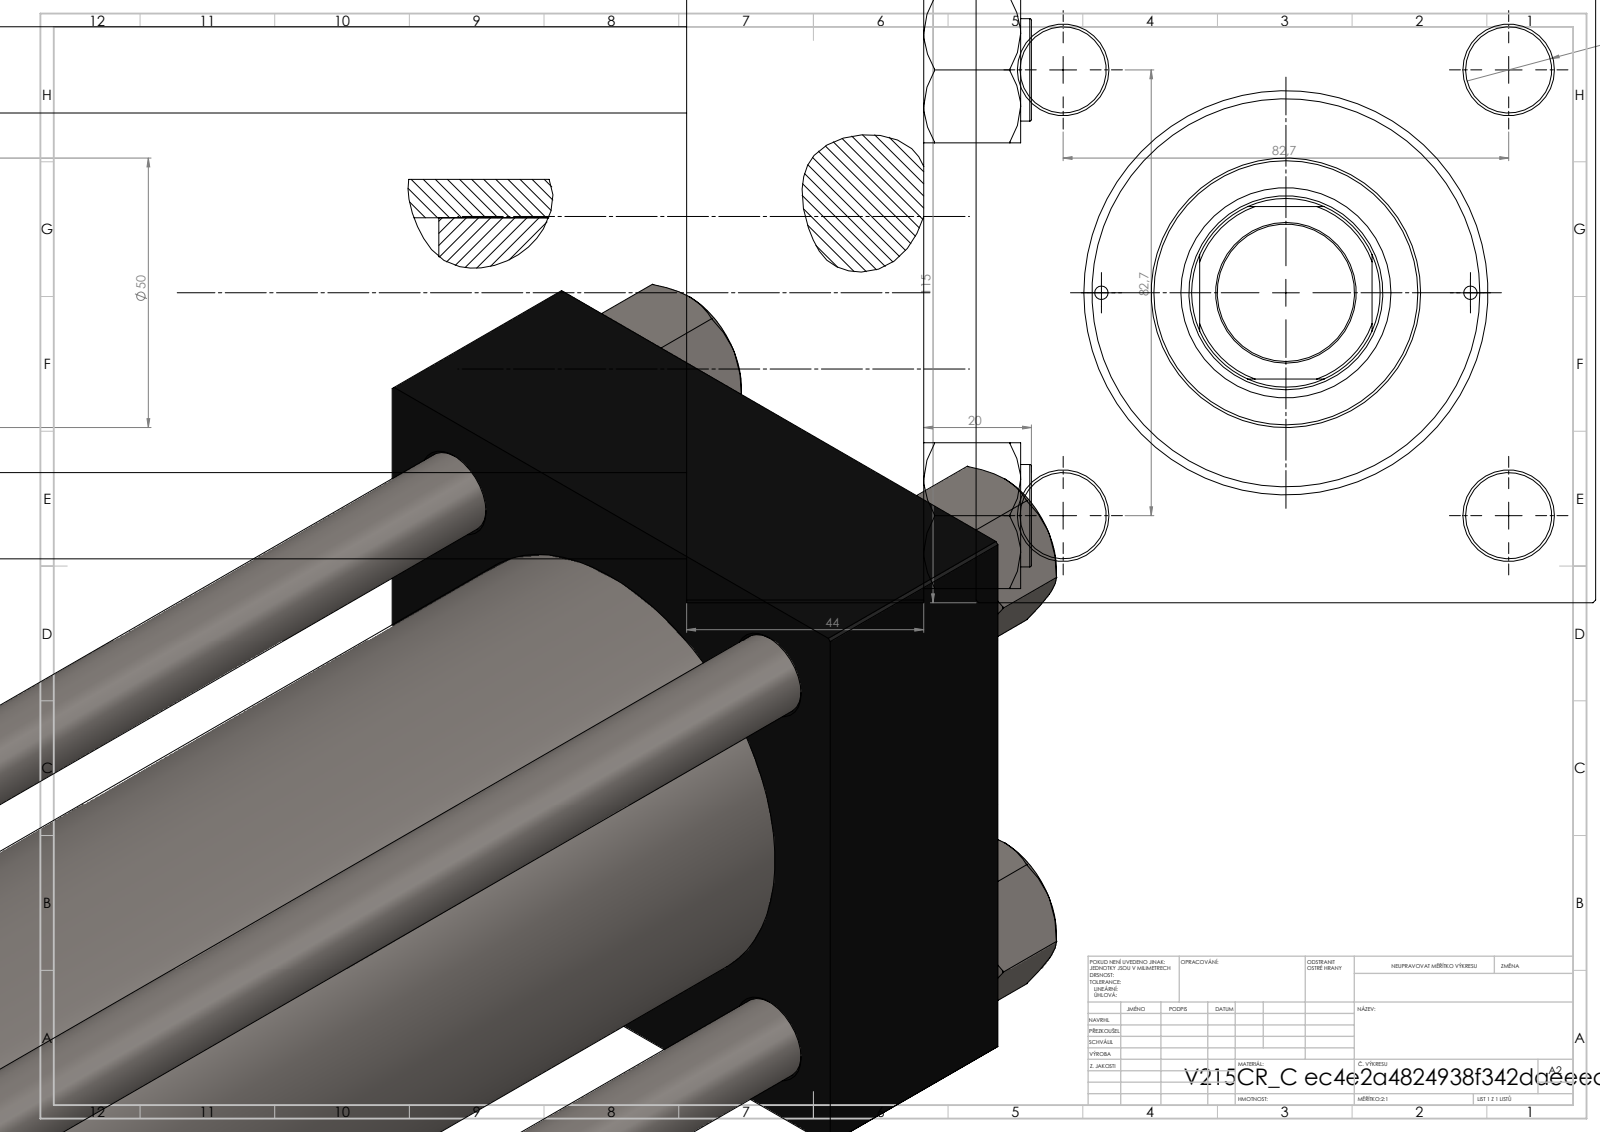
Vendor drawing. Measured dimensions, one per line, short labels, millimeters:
name: V215CR_C_Body; V215CR_C_TYCINKA; V215_VC_A; V215CR_VCP_C (+1 more)
written by: SolidWorks 2019 (CONFIG_CONTROL_DESIGN)
unit: mm
bodies: 11 solids, 1202 faces (576 planar, 90 cylindrical, 536 other)
size: 510 × 115 × 115
volume: 2 516 000 mm³; area: 502 497 mm²
holes: 4× ⌀16, 2× ⌀2.5, 2× ⌀7, 2× ⌀26.44, 2× ⌀35, 1× ⌀25.5, 1× ⌀36, 1× ⌀39, 1× ⌀61, 1× ⌀72, 1× ⌀80
bosses: 4× ⌀19, 1× ⌀86, 1× ⌀50
rounds: 1× R17.5
face distances: 115, 44, 459, 415, 390, 346, 69, 430.3, 386.3, 40.3
hole spacings: 41.96, 58.48, 82.7, 86.17, 34.25, 116.96, 68.5, 391
